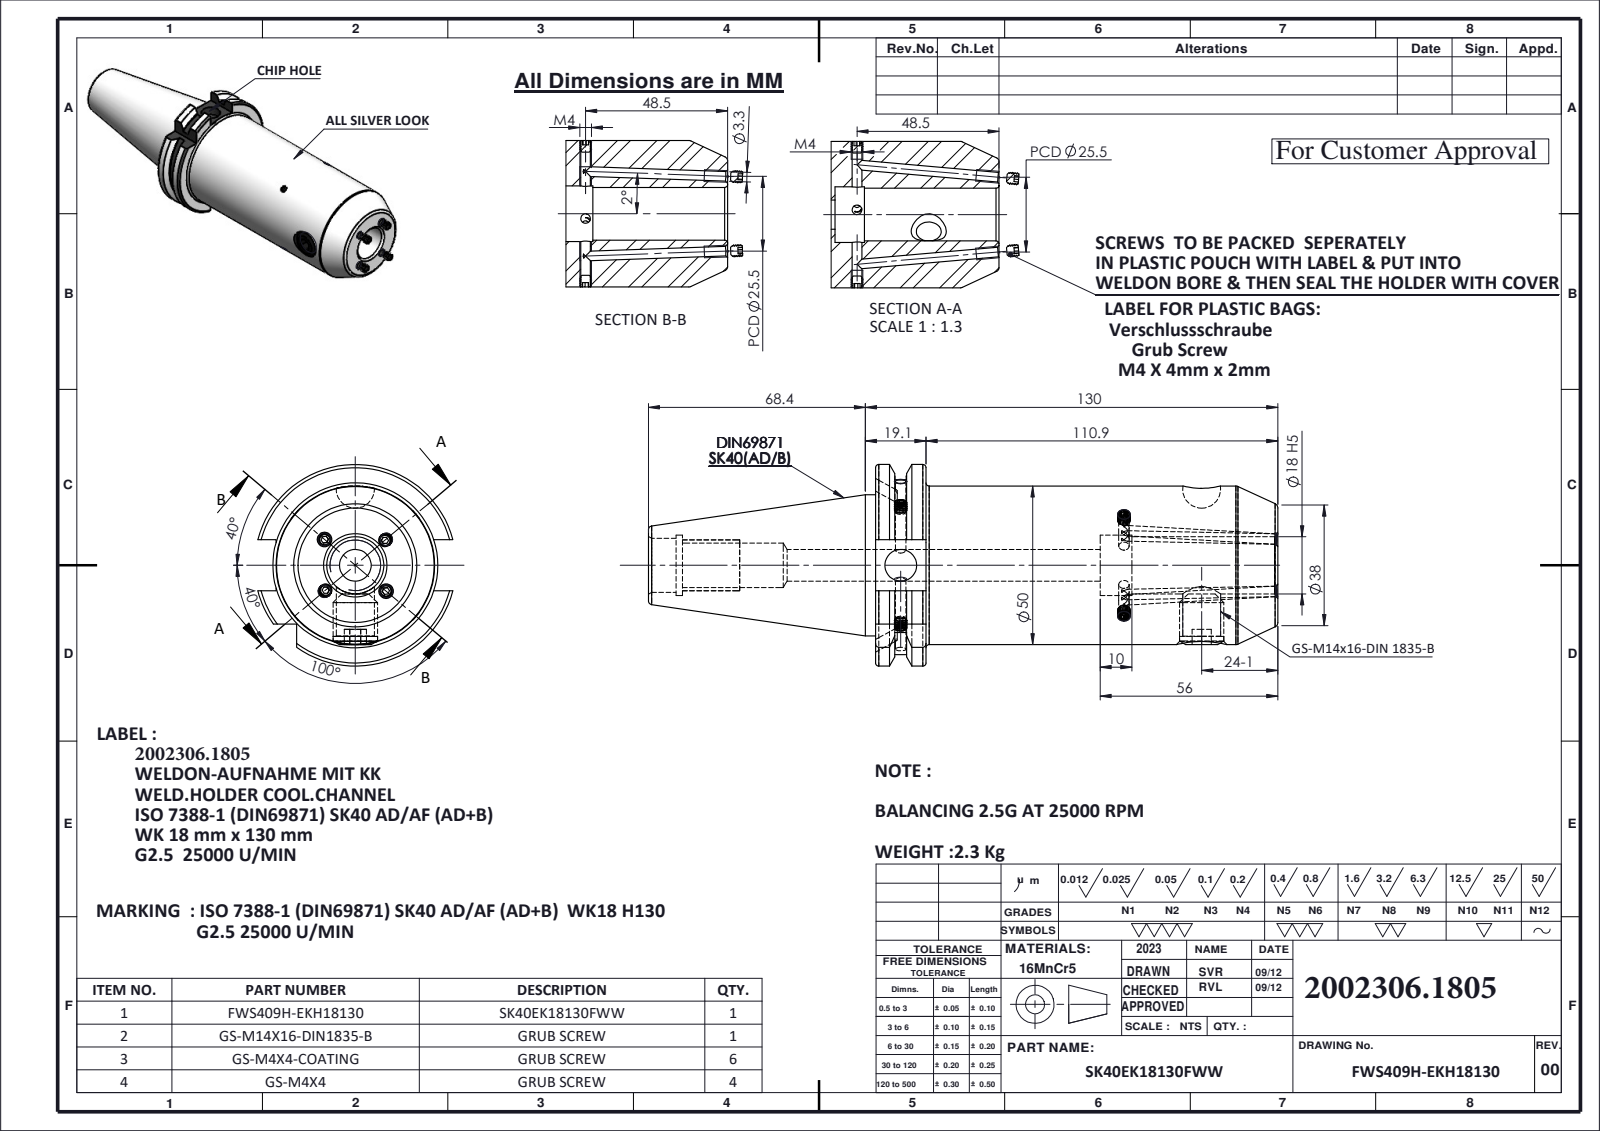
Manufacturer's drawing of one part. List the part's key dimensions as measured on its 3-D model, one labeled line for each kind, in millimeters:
Part name (STEP PRODUCT): GS-M14X16-DIN1835-B_ISO 4026 - M12 x 12-N; FWS409H-EKH18130; SK40EK18130FWW; GS-M4X4-COATING_DIN 913 - M4 x 4-N (+1 more)
STEP written by: SolidWorks 2023 (CONFIG_CONTROL_DESIGN)
Units: millimetres
Bodies: 12 solids, 641 faces (133 planar, 168 cylindrical, 340 other)
Overall size (bounding box): 205.2 × 63.55 × 61.48
Volume: 292 766 mm³ · Surface area: 47 314 mm²
Round holes (diameter × count): ⌀3.3 ×9, ⌀10 ×2, ⌀14 ×2, ⌀12 ×1, ⌀17 ×1, ⌀18 ×1, ⌀19 ×1
Round bosses / shafts (diameter × count): ⌀4 ×10, ⌀50 ×1, ⌀44.45 ×1
Partial cylindrical surfaces — rounded edges, fillets, slot ends (radius × count): R28.12 ×1, R31.77 ×1
Main face-to-face distances: 15.9, 126.8, 110.9, 70.8, 54.9, 56, 16.1, 47.8, 6.5, 71.6
